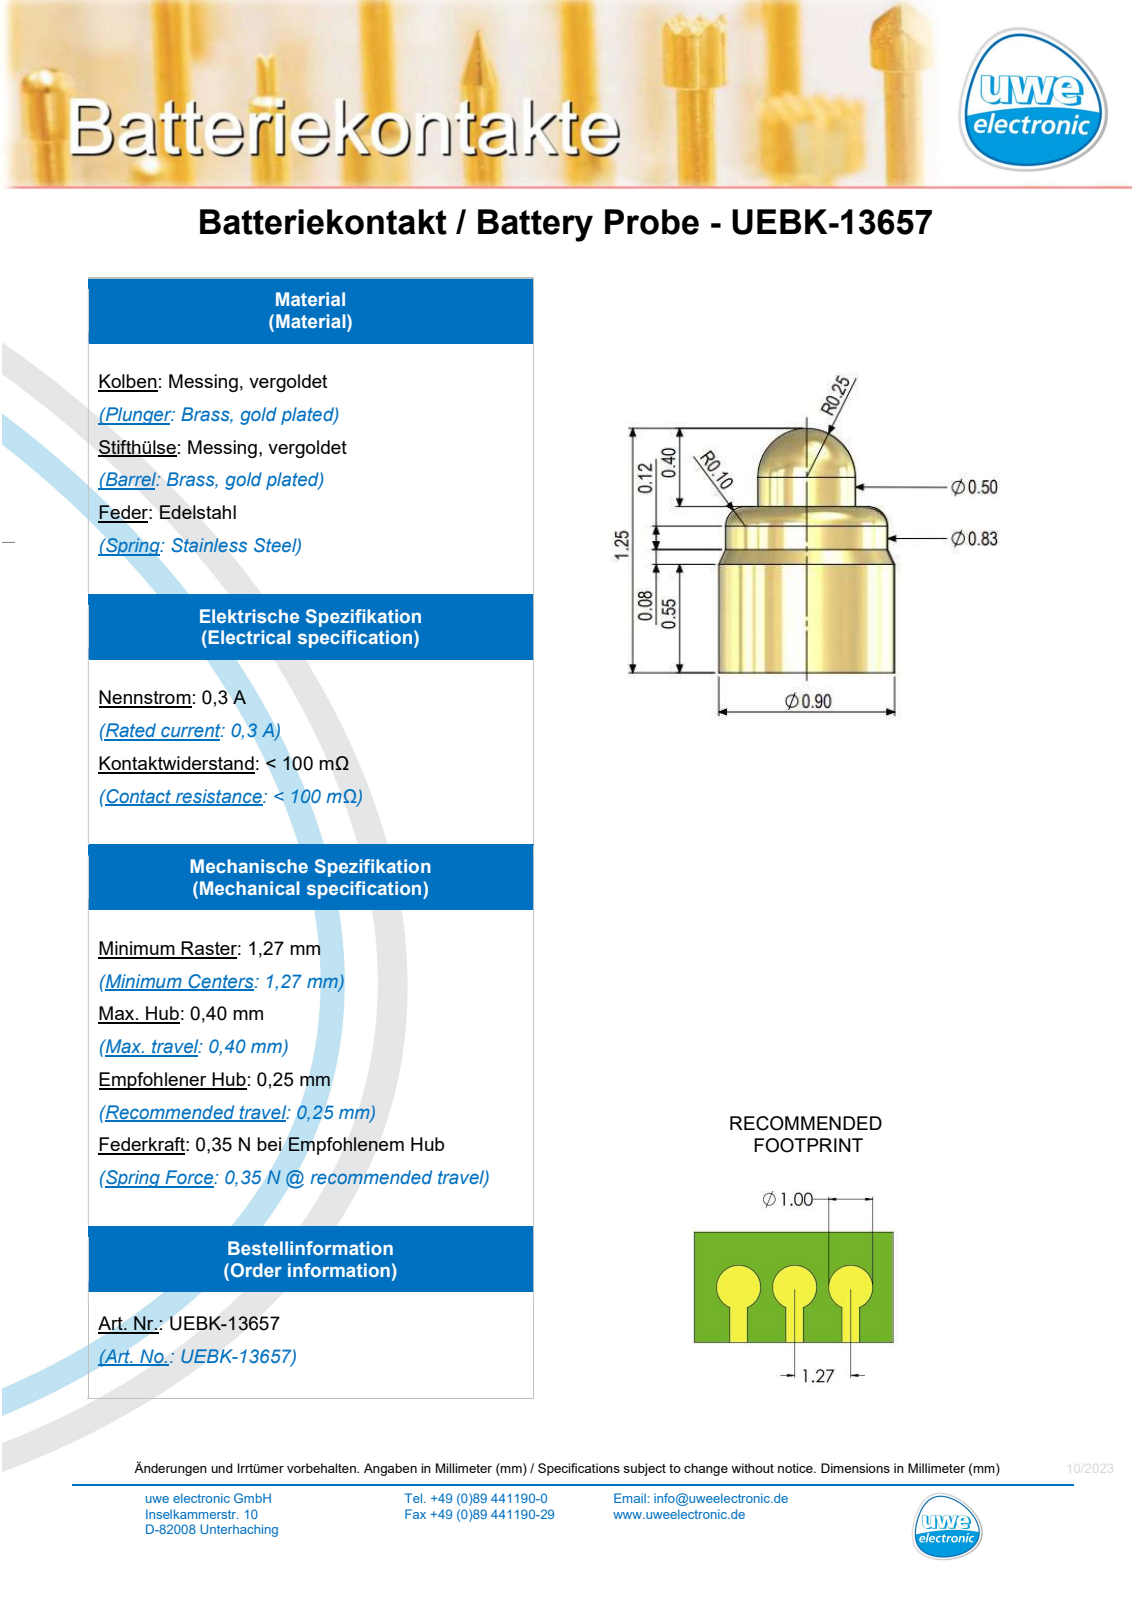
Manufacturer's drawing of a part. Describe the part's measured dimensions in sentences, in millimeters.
The part is named "UEBK-13657_step". Its 3-D file was written by "SolidWorks 2022 (AUTOMOTIVE_DESIGN)". It is 1 solid with 13 faces: 2 planar, 6 cylindrical and 5 other. Overall it measures 1.25 by 0.9 by 0.9 millimeters. Its volume is 0.573 cubic millimeters and its surface area 4 square millimeters. Round bosses or shafts: 1 of diameter 0.9, 1 of diameter 0.83, 1 of diameter 0.5. The main face-to-face distances are 0.85.
